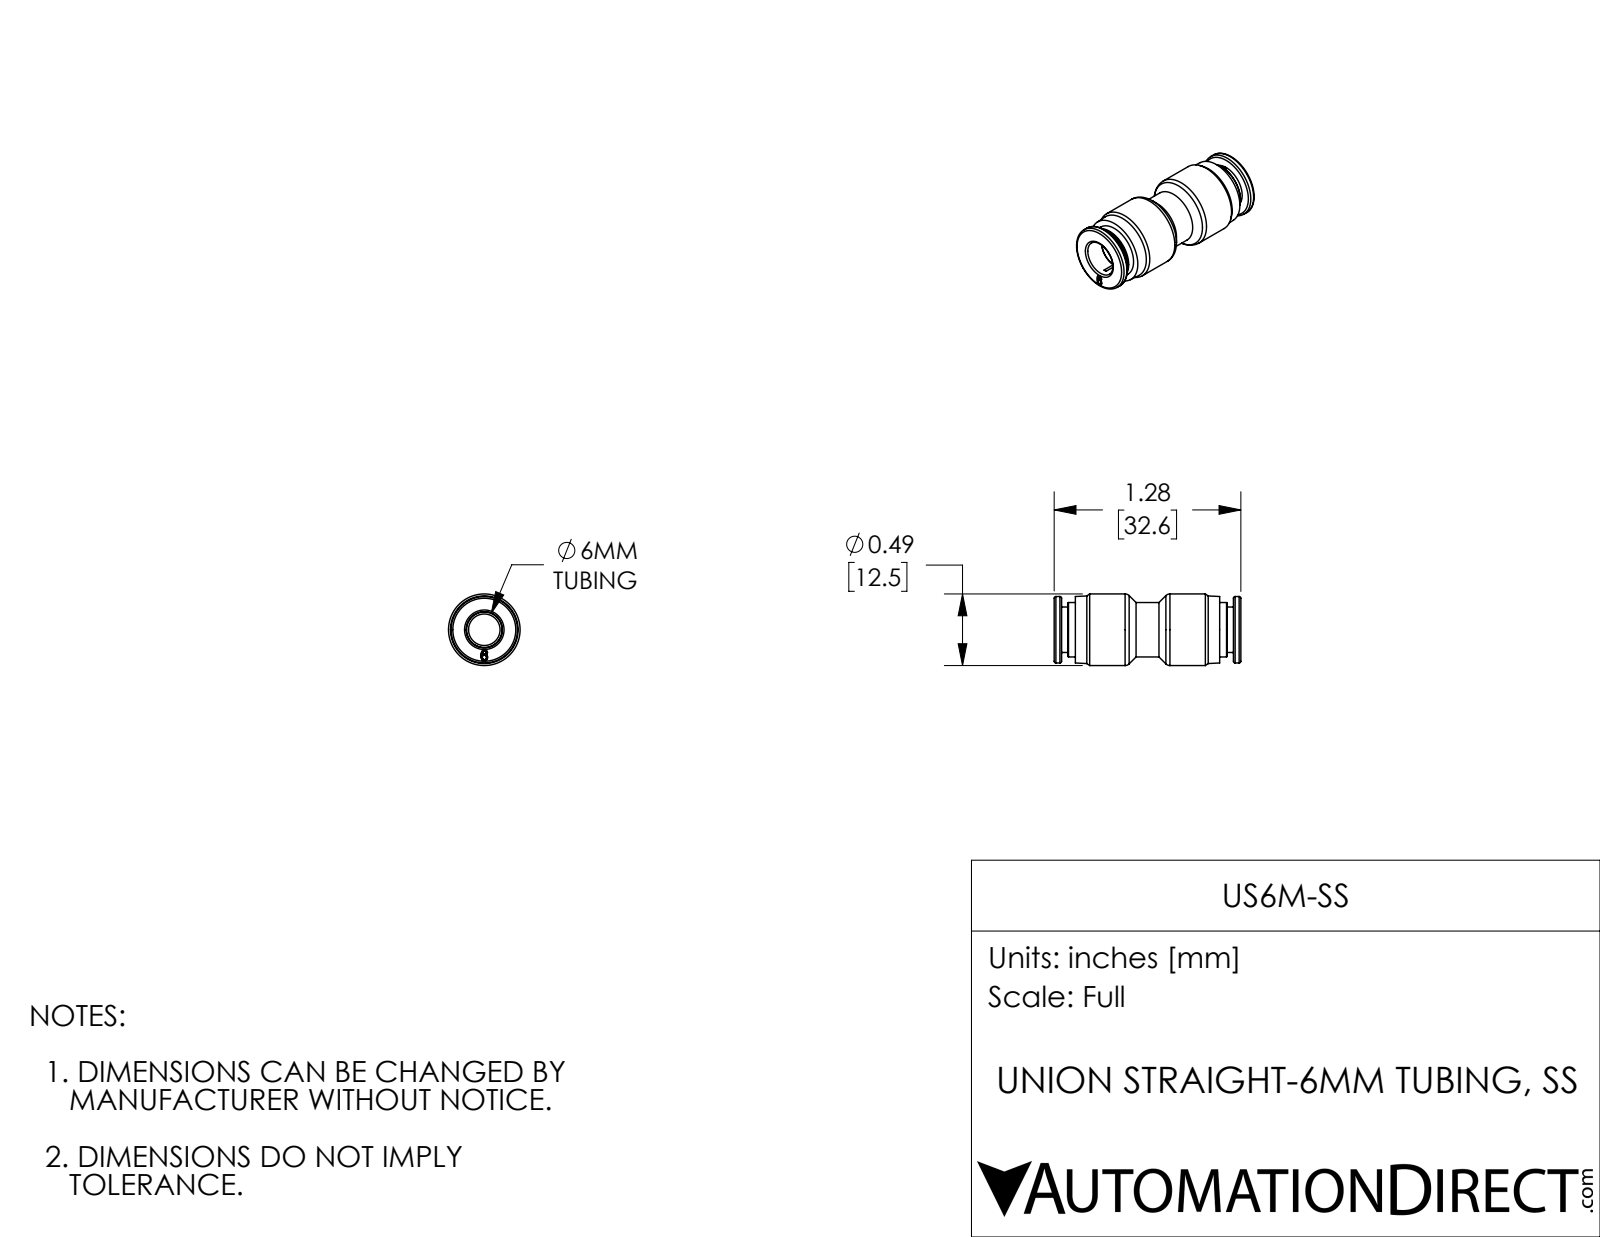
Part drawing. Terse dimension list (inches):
name: US6M-SS
written by: SolidWorks 2017 (AUTOMOTIVE_DESIGN)
unit: in
bodies: 1 solid, 130 faces (30 planar, 32 cylindrical, 68 other)
size: 1.283 × 0.492 × 0.492
volume: 0.14 in³; area: 3.61 in²
holes: 1× ⌀0.217, 1× ⌀0.244, 1× ⌀0.248, 1× ⌀0.319
bosses: 1× ⌀0.492, 1× ⌀0.457, 1× ⌀0.374, 1× ⌀0.313
face distances: 0.051, 0.094, 1.138, 1.232, 0.146, 1.087, 1.283, 1.181, 0.992, 0.043
